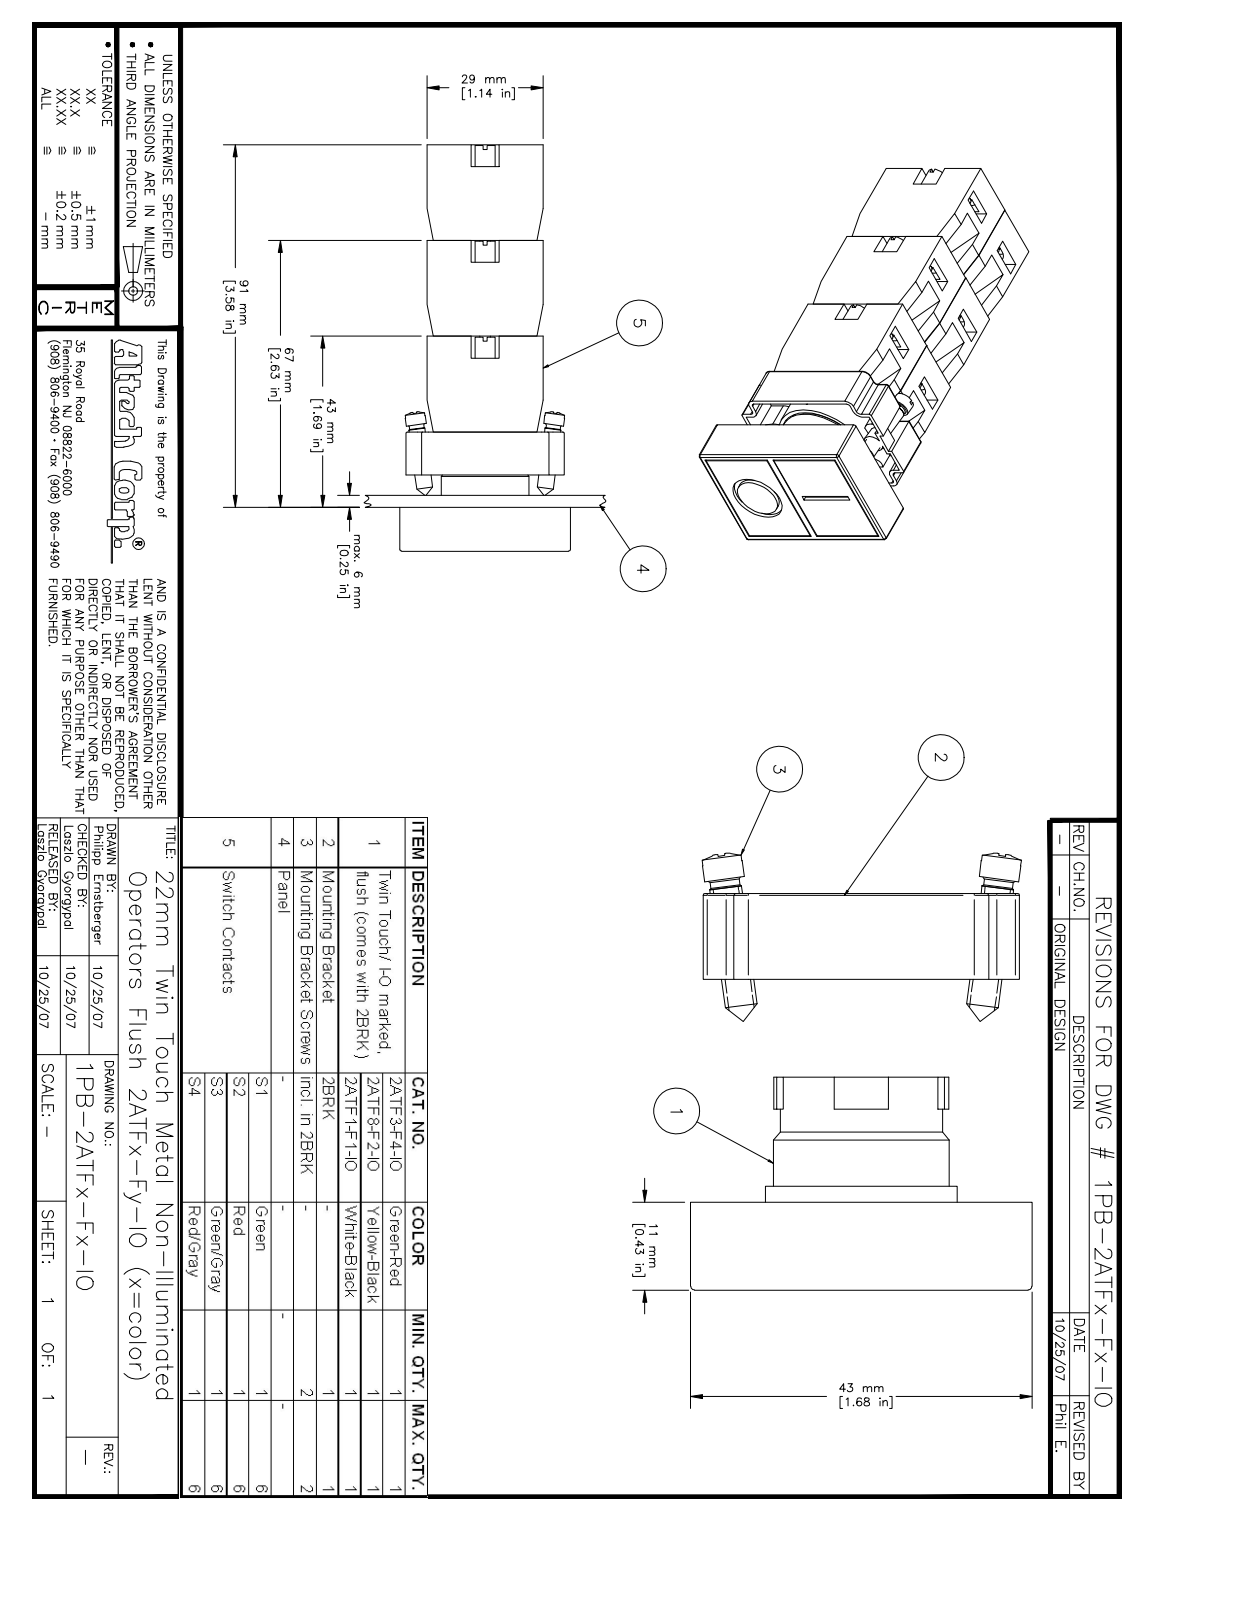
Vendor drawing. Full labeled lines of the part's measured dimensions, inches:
Part name (STEP PRODUCT): 2ATFx-Fx-IO_assembly; 2BRK; DIN 7985 (Z) M4x18-Z; S1 (+7 more)
STEP written by: Autodesk Inventor 2008 (AUTOMOTIVE_DESIGN)
Units: inches
Bodies: 30 solids, 1243 faces (691 planar, 195 cylindrical, 357 other)
Overall size (bounding box): 4.012 × 2.38 × 1.772
Volume: 4.965 in³ · Surface area: 74.82 in²
Round holes (diameter × count): ⌀0.098 ×5, ⌀0.102 ×2, ⌀0.531 ×1, ⌀0.866 ×1, ⌀0.876 ×1, ⌀0.886 ×1
Round bosses / shafts (diameter × count): ⌀0.118 ×6, ⌀0.197 ×4, ⌀0.108 ×4, ⌀0.059 ×4, ⌀0.157 ×2, ⌀0.144 ×2, ⌀0.955 ×1, ⌀0.945 ×1
Partial cylindrical surfaces — rounded edges, fillets, slot ends (radius × count): R0.039 ×13, R0.02 ×12, R0.01 ×11, R0.028 ×8, R0.089 ×5, R0.031 ×4, R0.071 ×4, R0.079 ×4
Main face-to-face distances: 0.583, 0.579, 0.945, 0.118, 1.161, 1.89, 1.142, 0.433, 2.516, 2.634
Hole centre spacings: 0.572, 0.257, 0.259, 0.512, 0.536, 0.845, 1.019, 1.024
